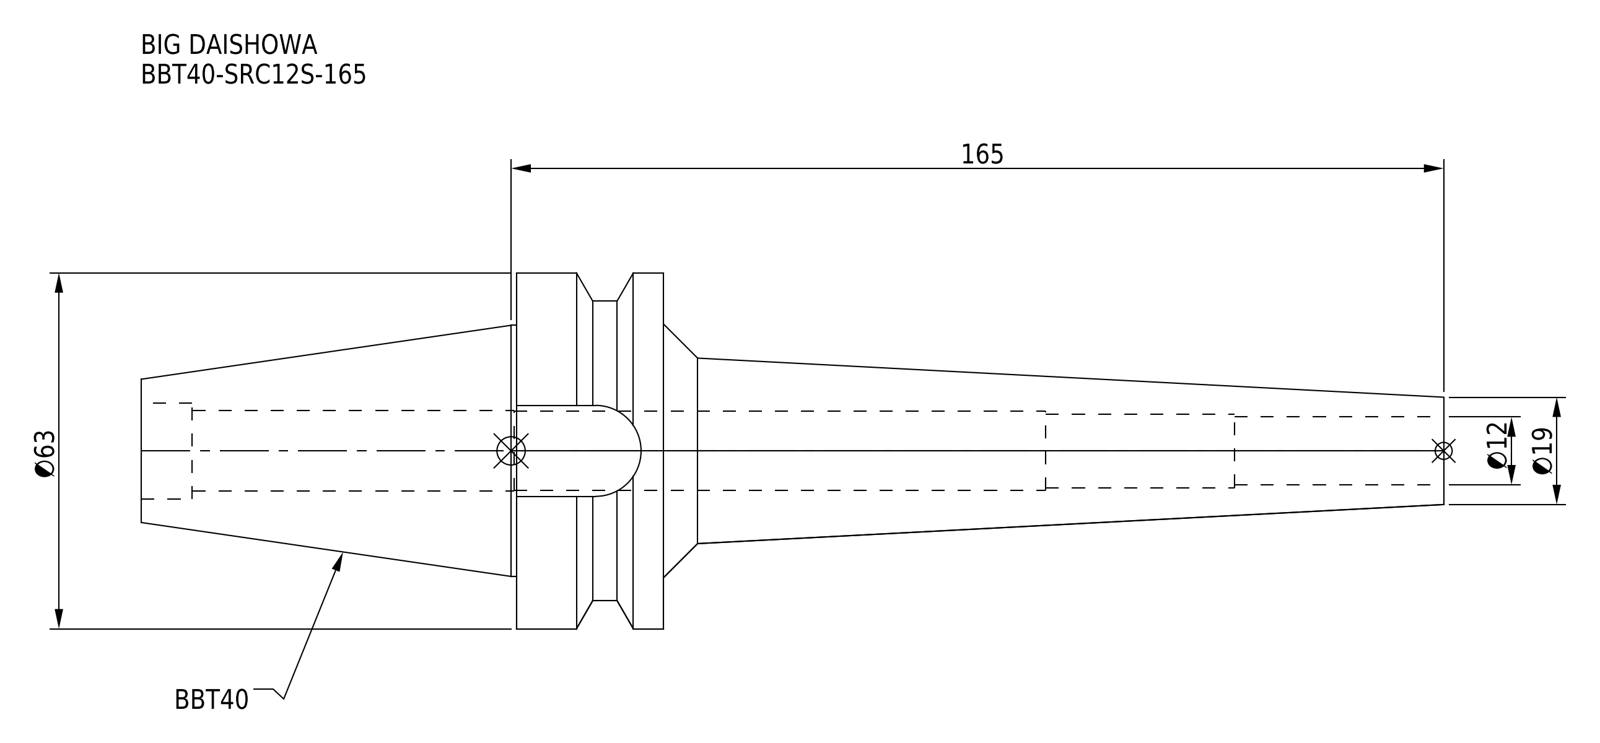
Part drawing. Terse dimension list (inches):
name: BBT40-SRC12S-165
written by: CREO PARAMETRIC BY PTC INC, 2016380 (AUTOMOTIVE_DESIGN)
unit: in
bodies: 1 solid, 46 faces (14 planar, 22 cylindrical, 10 other)
size: 9.071 × 2.48 × 2.48
volume: 10.98 in³; area: 60.46 in²
holes: 1× ⌀0.472, 1× ⌀0.512, 1× ⌀0.551, 1× ⌀0.559, 1× ⌀0.669
bosses: 1× ⌀2.48, 1× ⌀2.087, 1× ⌀1.75
rounds: 1× R0.317
face distances: 1.024, 1.772, 3.638, 2.614, 0.634, 5.433, 6.457, 9.071, 8.717, 3.283
